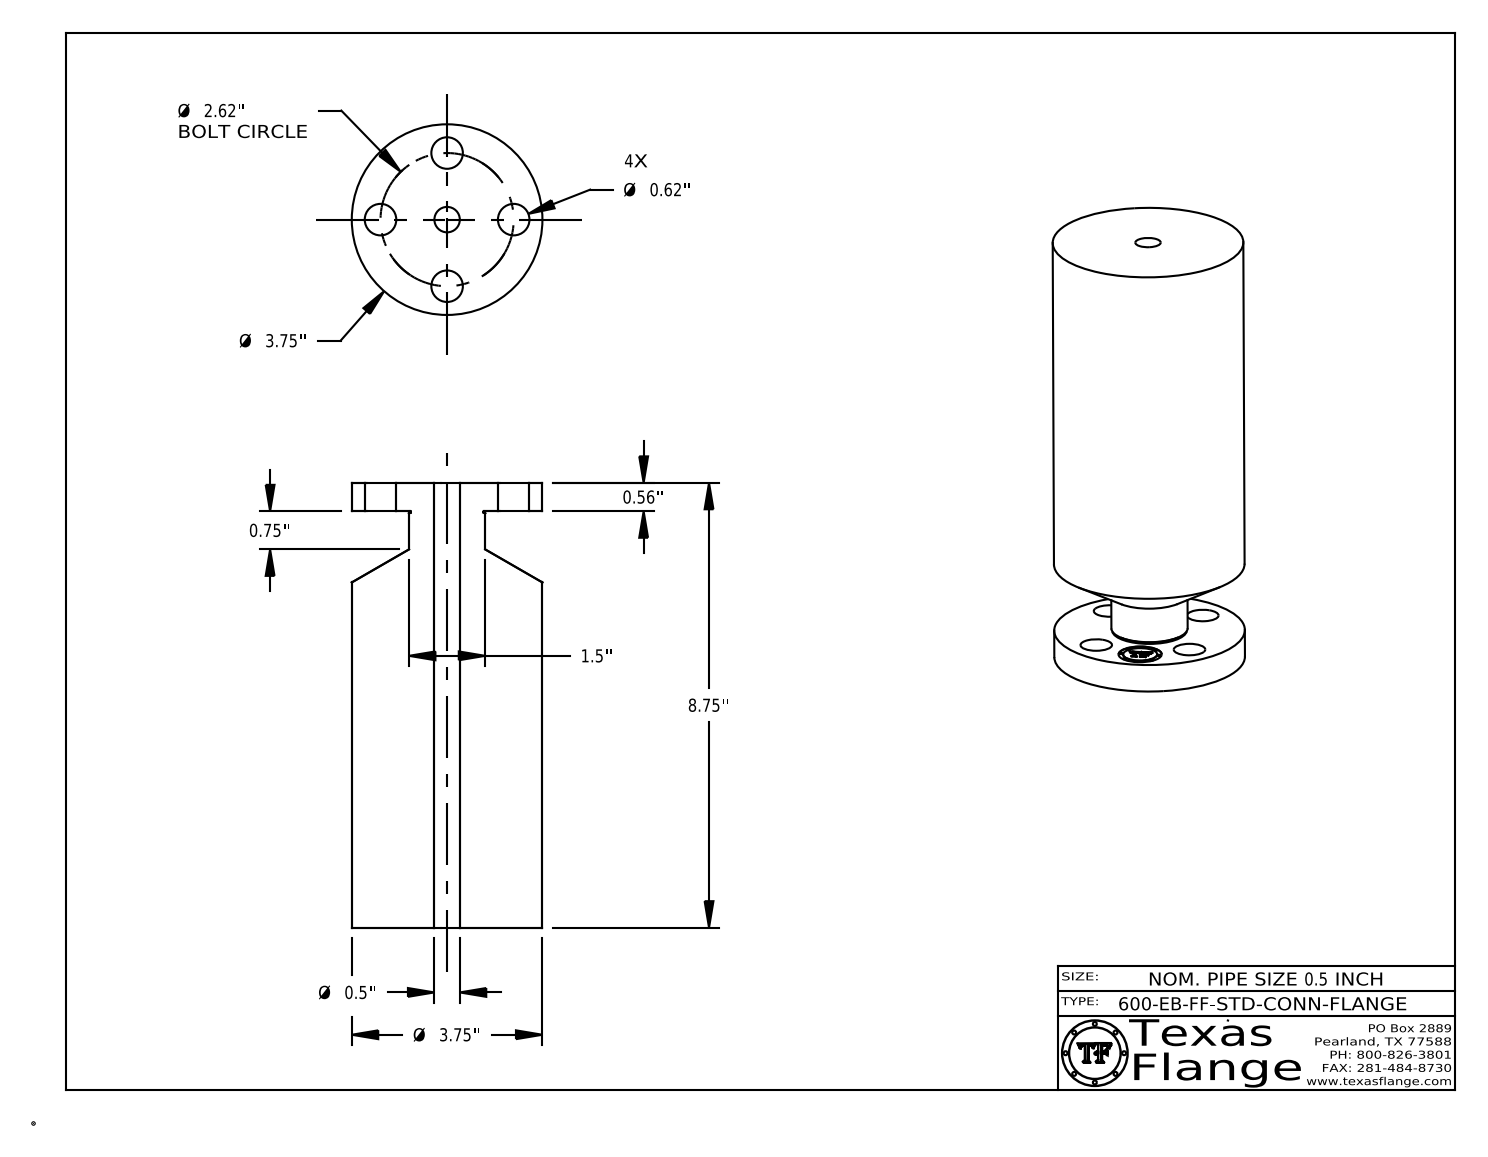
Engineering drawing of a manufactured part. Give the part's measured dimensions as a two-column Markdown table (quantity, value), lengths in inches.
| quantity | value |
| --- | --- |
| part name | 0.5-600-EB-FF-STD-CONN-FLANGE |
| STEP written by | CATIA V5 STEP AP214 (AUTOMOTIVE_DESIGN) |
| units | inches |
| bodies | 1 solid, 410 faces (368 planar, 36 cylindrical, 6 other) |
| overall size | 8.75 × 3.75 × 3.75 |
| volume | 83.84 in³ |
| surface area | 147.7 in² |
| round holes (diameter × count) | 0.62 × 4, 0.5 × 1, 0.85 × 1 |
| round bosses / shafts (diameter × count) | 0.051 × 8, 3.75 × 1, 1.5 × 1, 0.67 × 1 |
| main face-to-face distances | 8.75, 0.56, 8.19, 0.555, 8.195, 0.254, 0.248, 0.016, 0.046, 0.165 |
| hole center spacings | 1.31, 1.852, 1.003, 2.42, 2.62, 1.31 |
